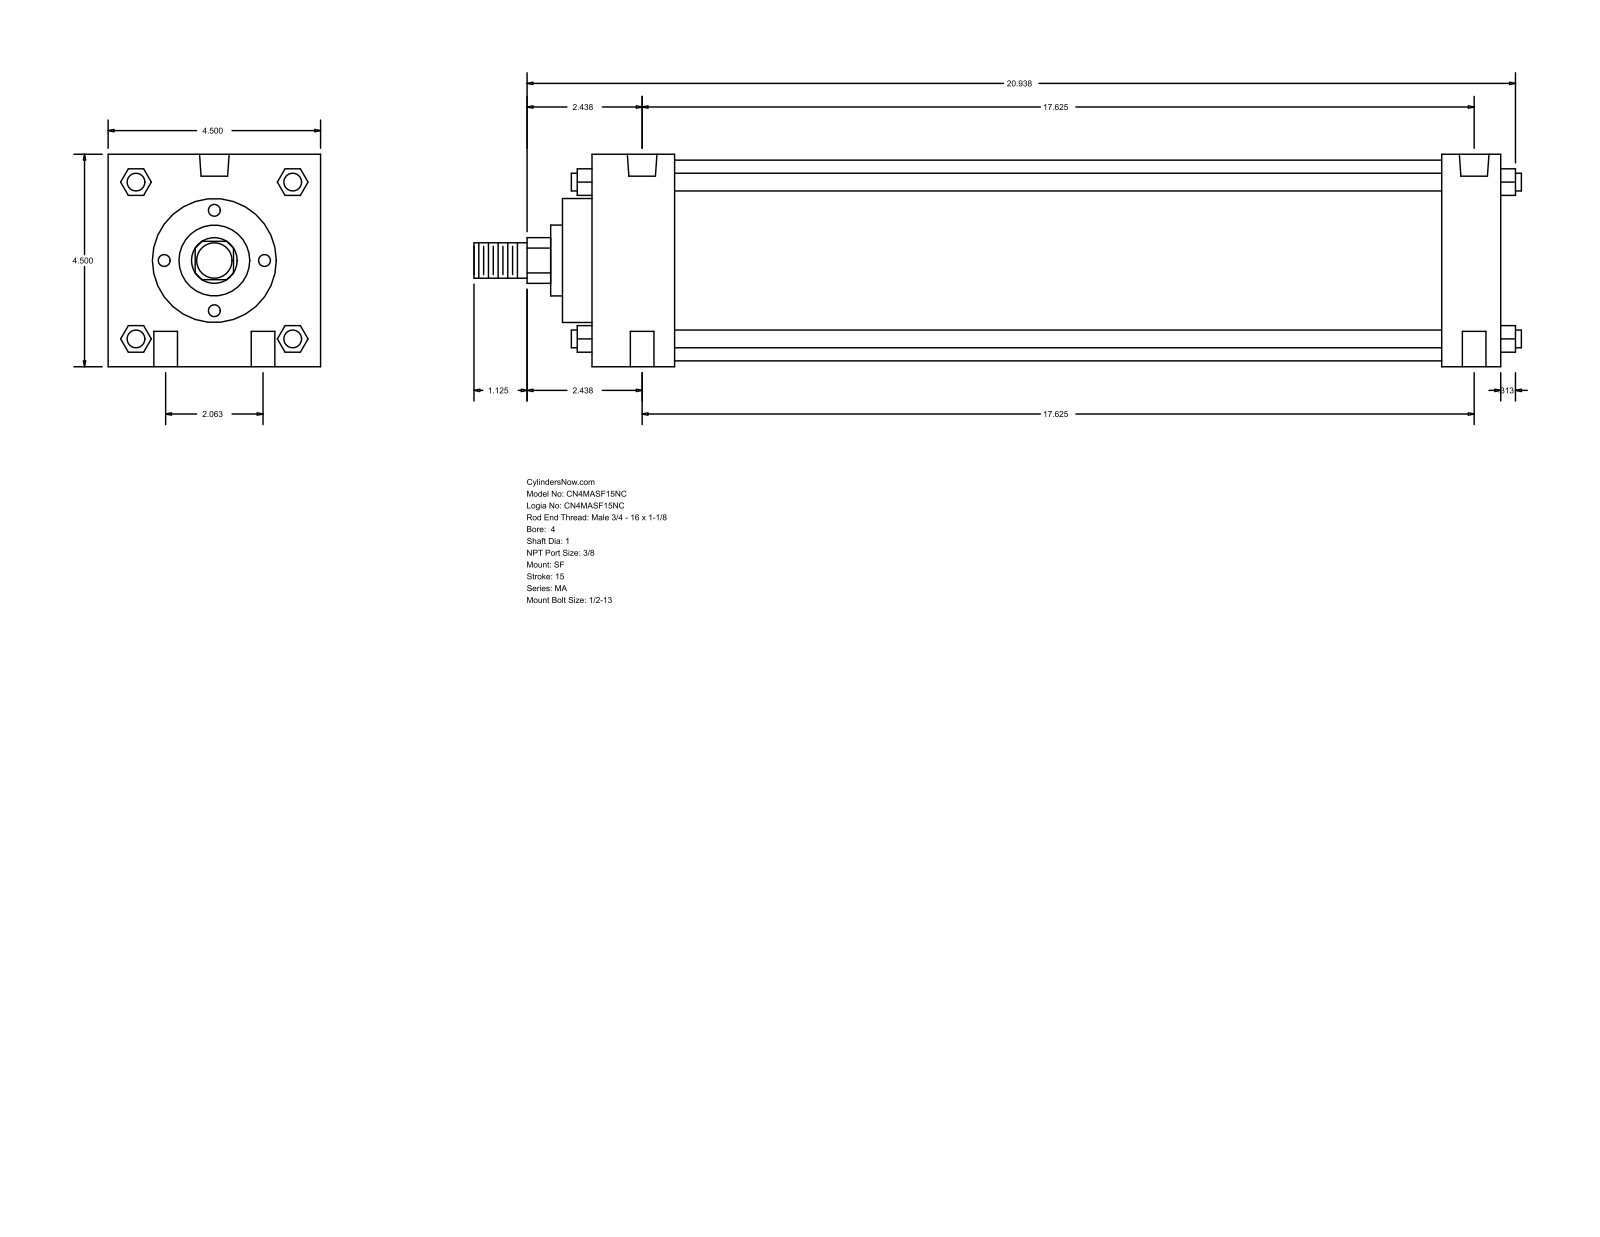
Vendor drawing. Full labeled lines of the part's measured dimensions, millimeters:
Part name (STEP PRODUCT): MA_SF__0400_1
STEP written by: GSSL Pune (CONFIG_CONTROL_DESIGN)
Units: millimetres
Bodies: 0 solids, 126 faces (95 planar, 31 cylindrical, 0 other)
Overall size (bounding box): 563.56 × 114.3 × 114.3
Round holes (diameter × count): ⌀12.7 ×4, ⌀11.11 ×2, ⌀15.93 ×2
Round bosses / shafts (diameter × count): ⌀9.53 ×4, ⌀107.95 ×1, ⌀66.67 ×1, ⌀38.1 ×1, ⌀25.4 ×1, ⌀19.05 ×1
Partial cylindrical surfaces — rounded edges, fillets, slot ends (radius × count): R12.29 ×1
Main face-to-face distances: 114.3, 488.96, 457.2, 31.76, 44.46, 412.74, 444.5, 15.87, 60.33, 473.07
Hole centre spacings: 26.19, 448.45, 447.68, 52.38, 450.73, 438.15
